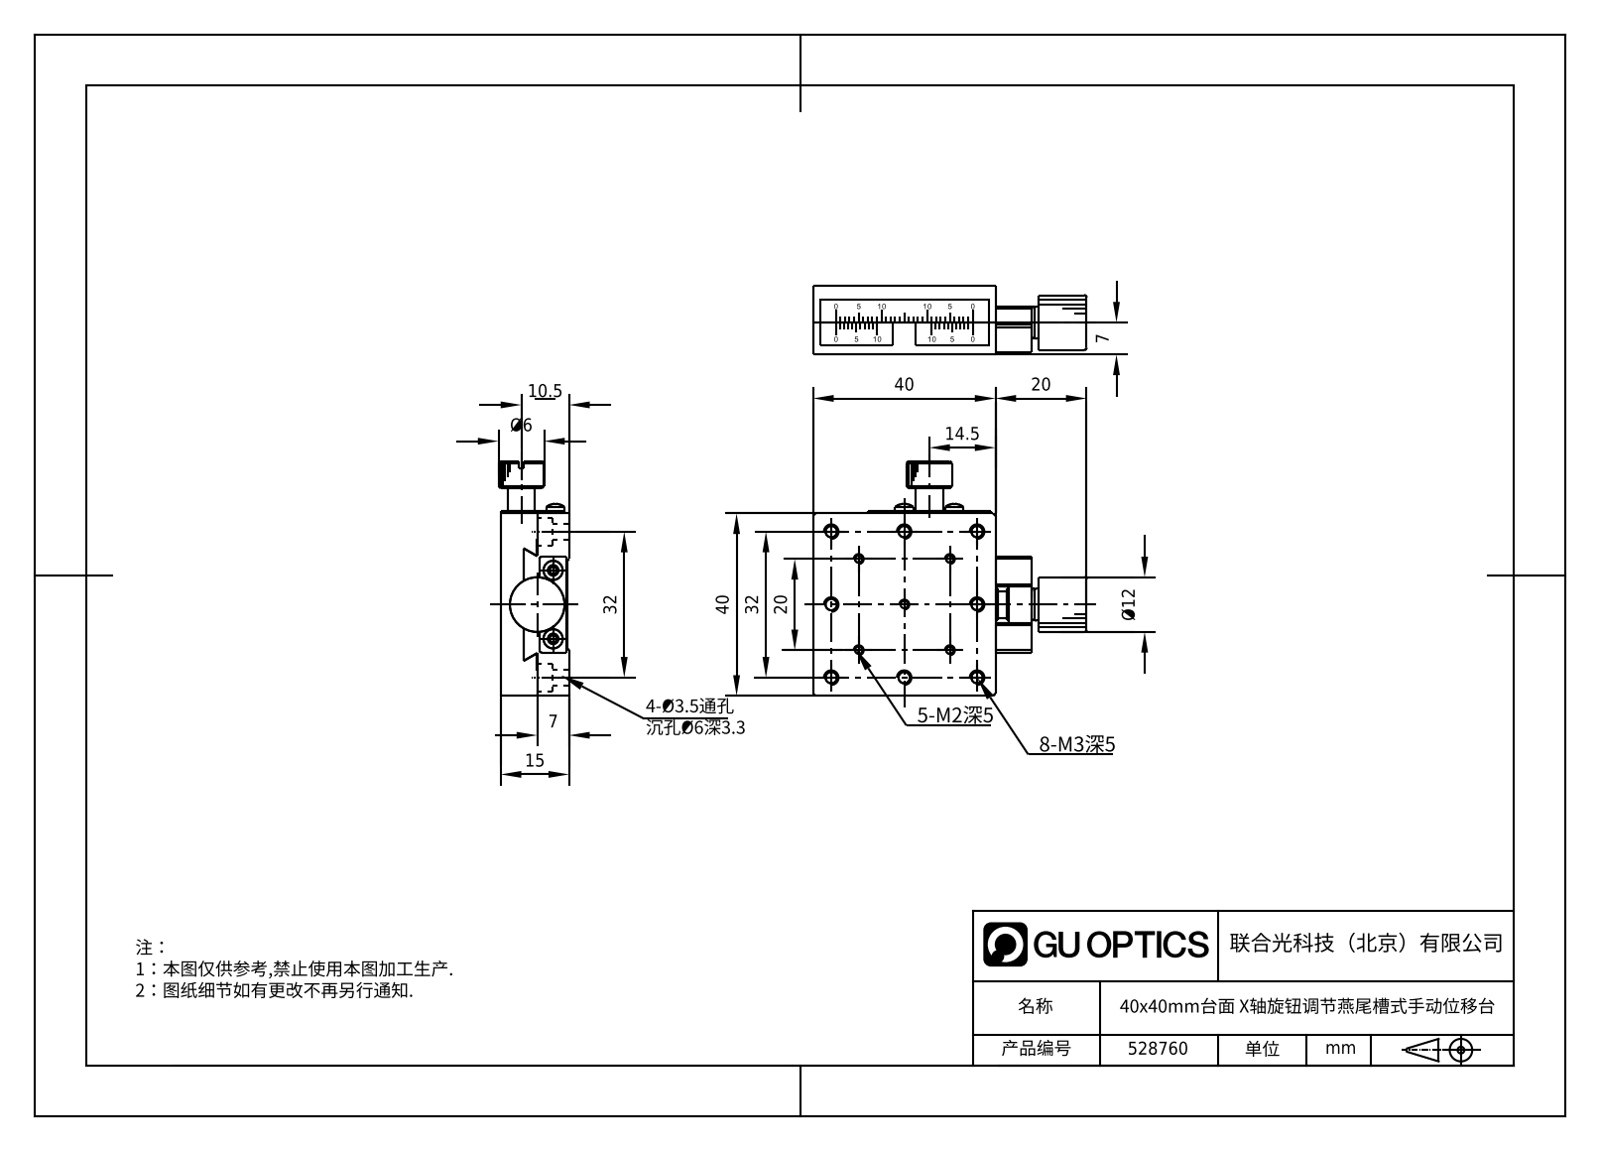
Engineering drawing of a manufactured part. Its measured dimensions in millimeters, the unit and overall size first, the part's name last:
Units: millimetres
Overall size (bounding box): 60 × 48.5 × 15
Round holes (diameter × count): ⌀1.57 ×12, ⌀2.5 ×10, ⌀2.46 ×6, ⌀4 ×6, ⌀3.5 ×4, ⌀6 ×4, ⌀2.46 ×3, ⌀1.57 ×2, ⌀2.01 ×1, ⌀3.24 ×1, ⌀5 ×1, ⌀7 ×1
Round bosses / shafts (diameter × count): ⌀6 ×2, ⌀4 ×2, ⌀3 ×1, ⌀2 ×1
Partial cylindrical surfaces — rounded edges, fillets, slot ends (radius × count): R1.5 ×4, R2 ×4, R1.25 ×2, R6 ×1
Main face-to-face distances: 8, 4, 15, 7, 3.5, 0.5, 40, 10.5, 3, 4.5
Hole centre spacings: 16, 11.66, 22.63, 26.68, 27.86, 35.78, 32, 8.49
Volume: 23 149 mm³ · Surface area: 14 626 mm²
Bodies: 3 solids, 494 faces (216 planar, 125 cylindrical, 153 other)
Part name (STEP PRODUCT): 528760
STEP written by: SolidWorks 2020 (CONFIG_CONTROL_DESIGN)
